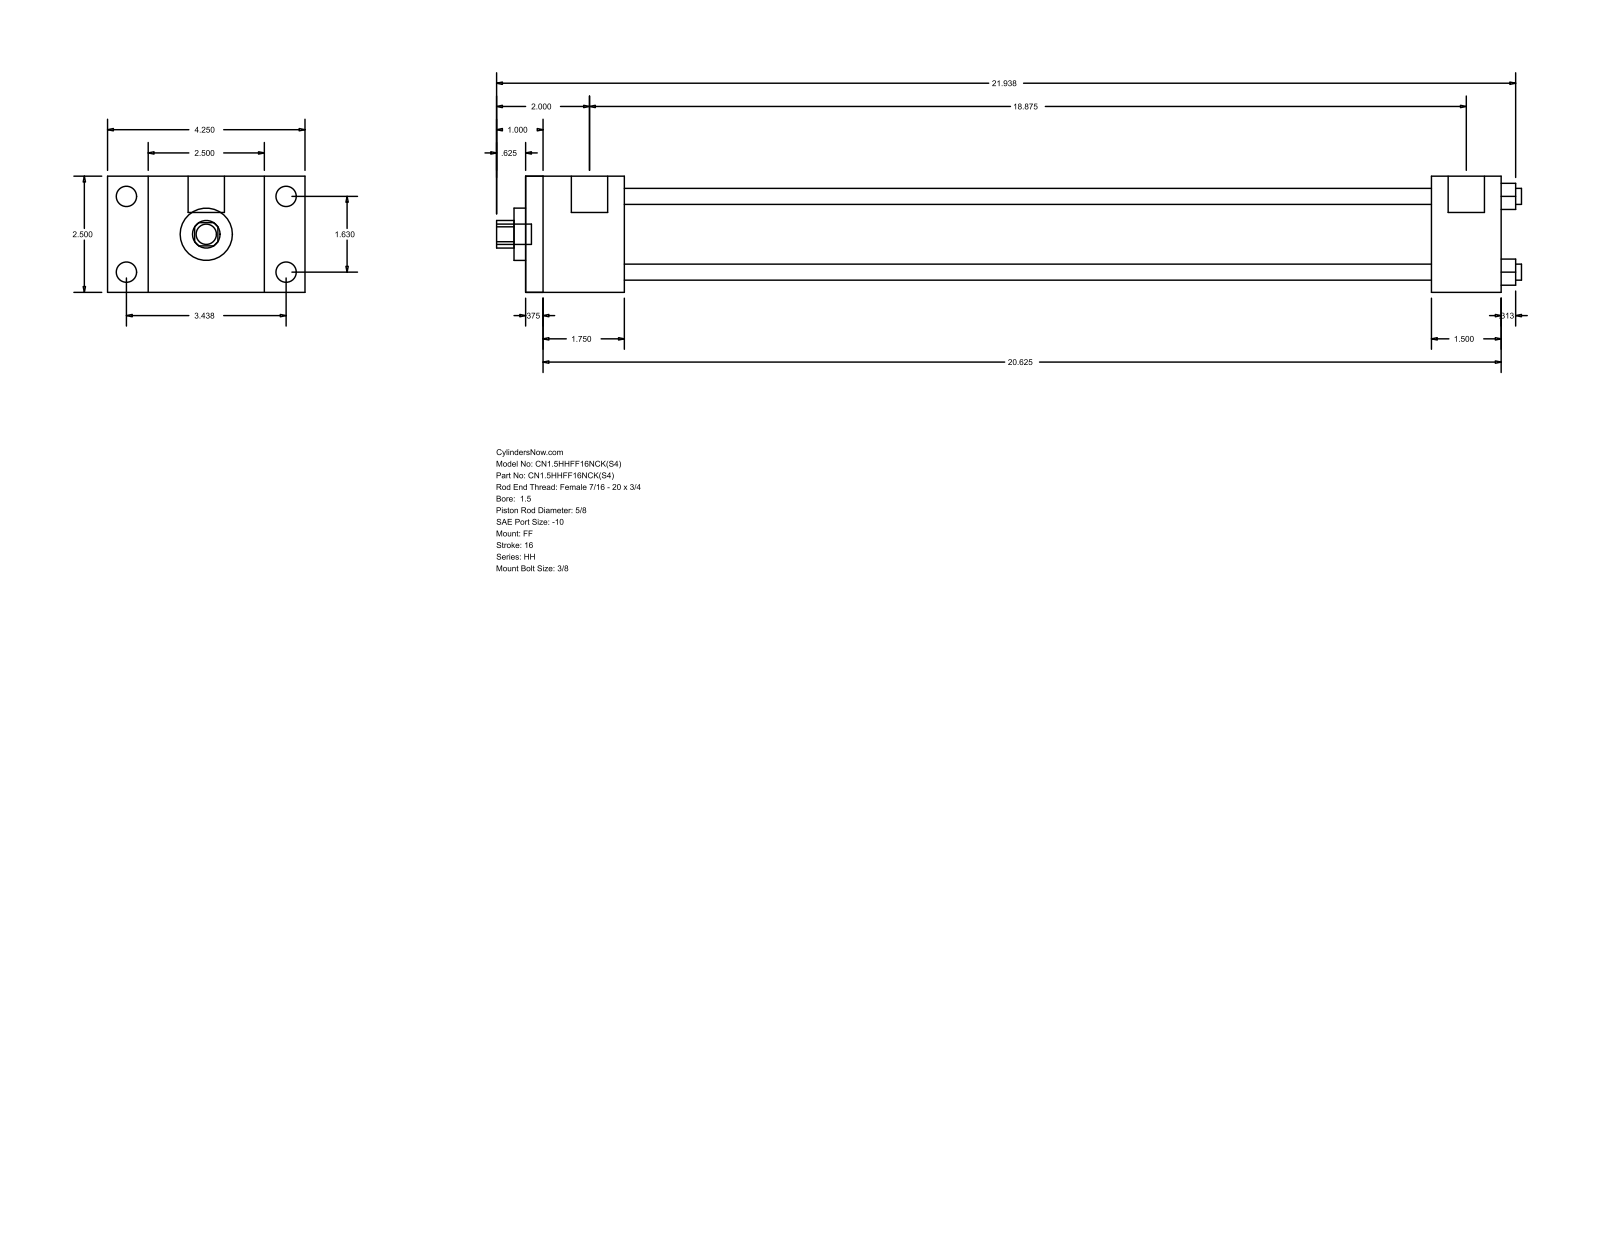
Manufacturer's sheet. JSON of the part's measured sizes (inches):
{"part_name": "HH_FF__0150_0.625", "step_written_by": "GSSL Pune (CONFIG_CONTROL_DESIGN)", "units": "inches", "bodies": {"solids": 0, "faces": 92, "planar": 64, "cylindrical": 28, "other": 0}, "overall_size": [22.063, 4.25, 2.5], "round_holes": [[0.345, 4], [0.625, 1], [1.125, 1], [1.75, 1]], "round_bosses_or_shafts": [[0.438, 4], [0.219, 4], [0.781, 2], [0.437, 1]], "partial_cylinders_radius": [[0.297, 1]], "face_to_face_distances": [2.5, 21, 0.375, 20.625, 2.125, 1.75, 18.875, 19.5, 19.125, 17.375], "hole_center_spacings": [1.152, 1.63, 2.305]}
